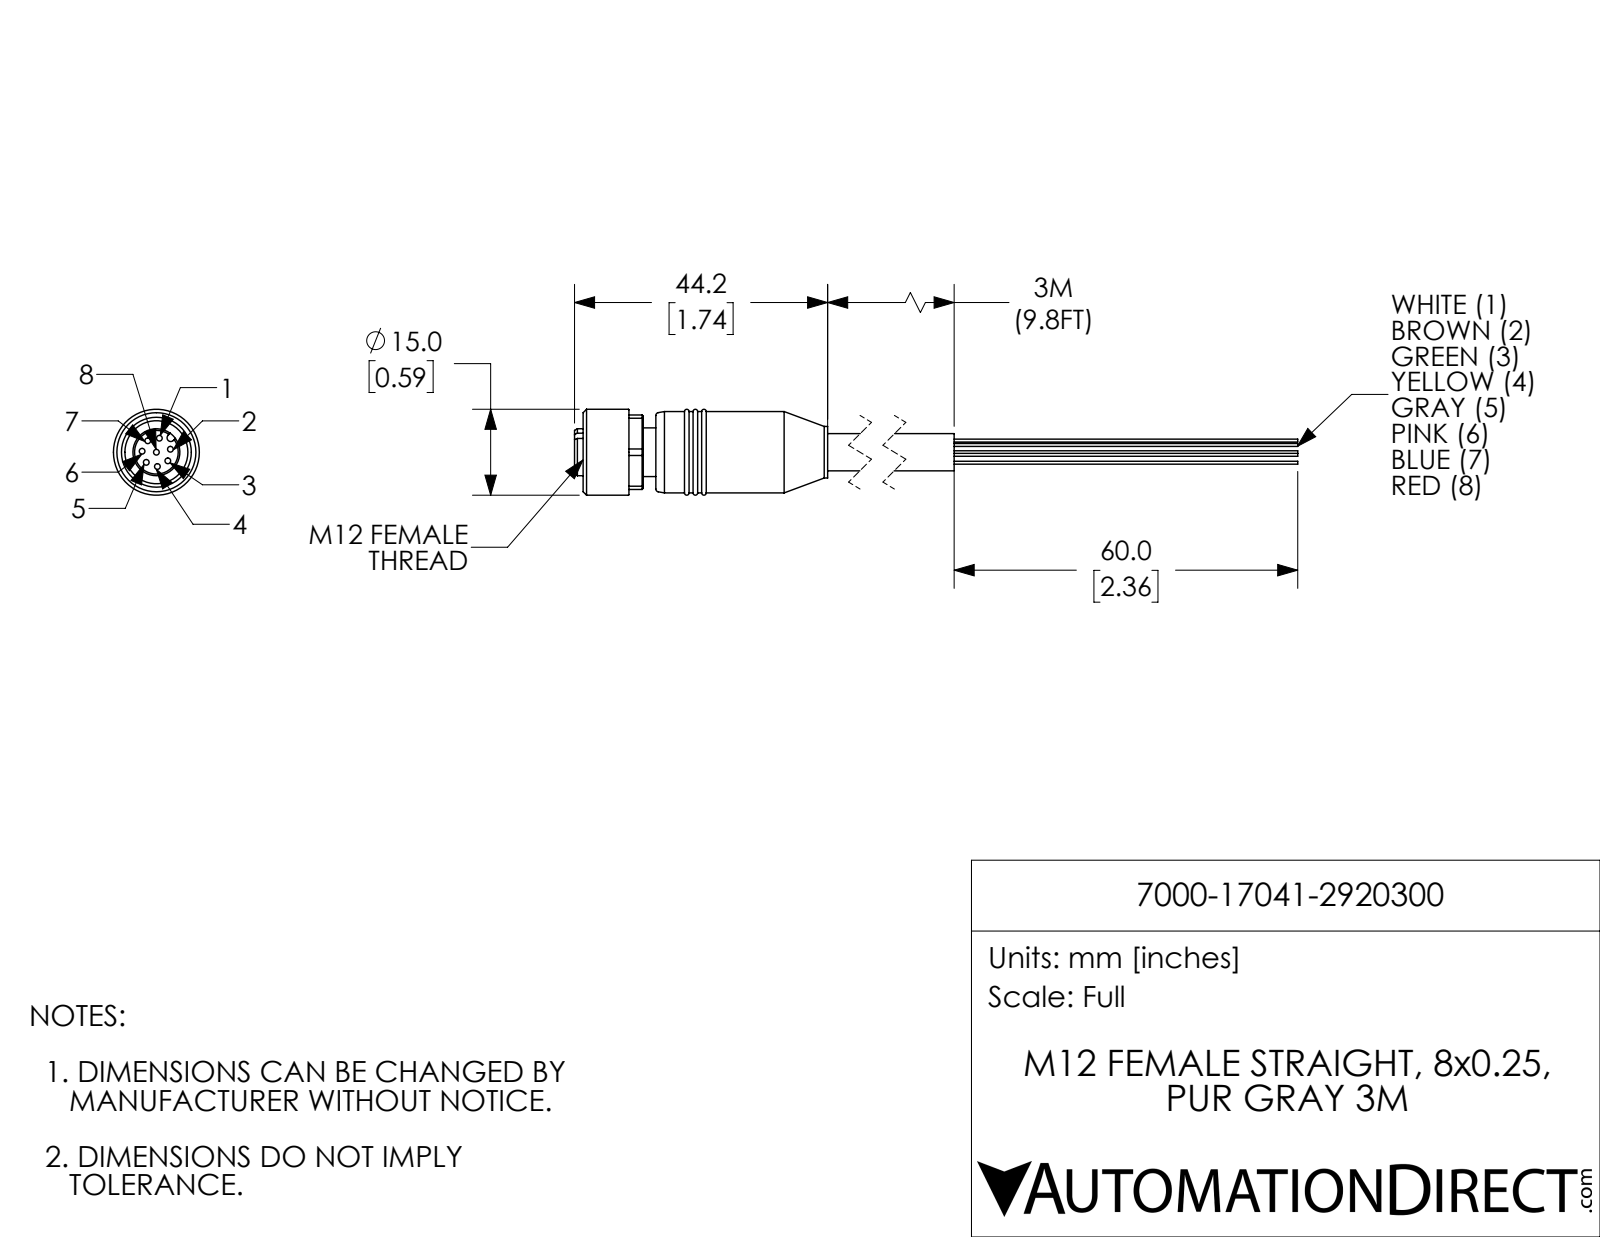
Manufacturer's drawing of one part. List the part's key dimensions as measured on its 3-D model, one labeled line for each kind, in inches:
Part name (STEP PRODUCT): 7000-17041-2920300
STEP written by: SolidWorks 2017 (AUTOMOTIVE_DESIGN)
Units: inches
Bodies: 1 solid, 131 faces (39 planar, 59 cylindrical, 33 other)
Overall size (bounding box): 4.89 × 0.591 × 0.591
Volume: 0.41 in³ · Surface area: 6.447 in²
Round holes (diameter × count): ⌀0.039 ×8, ⌀0.433 ×1
Round bosses / shafts (diameter × count): ⌀0.02 ×8, ⌀0.591 ×1, ⌀0.559 ×1, ⌀0.354 ×1, ⌀0.335 ×1, ⌀0.323 ×1, ⌀0.256 ×1
Partial cylindrical surfaces — rounded edges, fillets, slot ends (radius × count): R0.026 ×1, R0.283 ×1
Main face-to-face distances: 0.087, 0.512, 0.118, 0.205, 0.354, 0.472, 0.559, 0.098, 0.059, 0.295
Hole centre spacings: 0.098, 0.081, 0.149, 0.195, 0.082, 0.166, 0.189, 0.189
